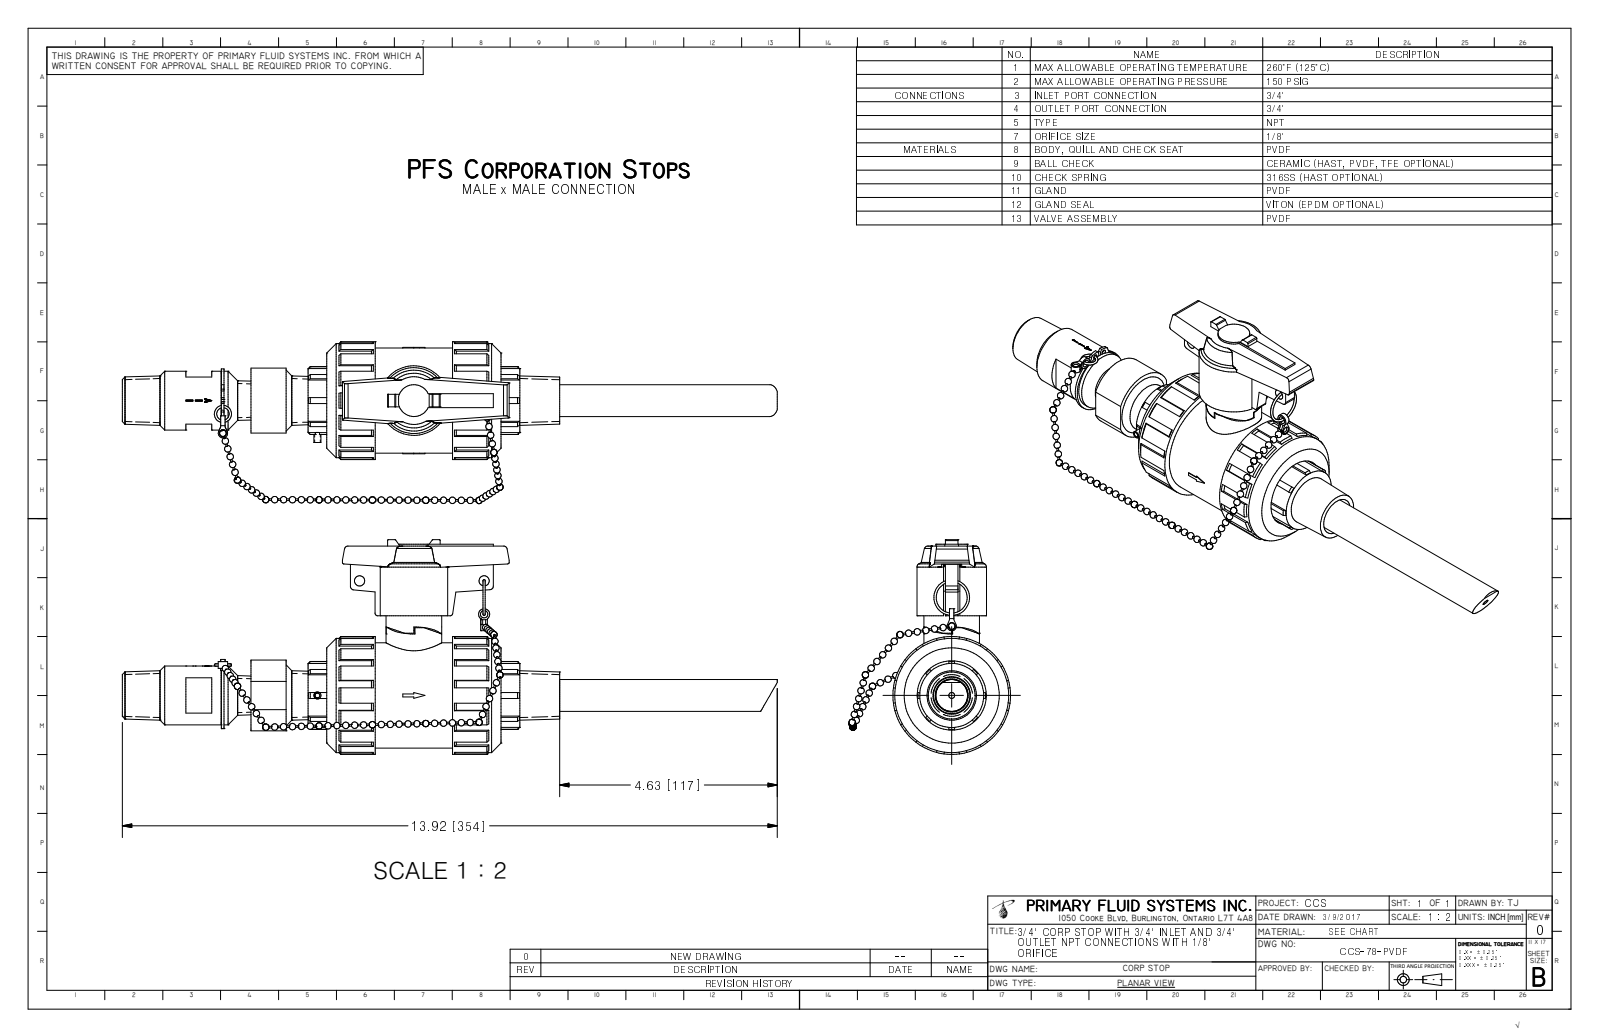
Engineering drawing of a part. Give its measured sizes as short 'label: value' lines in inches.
name: CCS-78-PVDF_R0
written by: Autodesk Inventor 2009 (AUTOMOTIVE_DESIGN)
unit: in
bodies: 1 solid, 613 faces (293 planar, 78 cylindrical, 242 other)
size: 13.922 × 4.554 × 3.436
volume: 26.76 in³; area: 125.7 in²
holes: 1× ⌀0.098, 1× ⌀0.125, 1× ⌀0.217, 1× ⌀0.25, 1× ⌀0.469, 1× ⌀0.56, 1× ⌀1.47, 1× ⌀2.16
bosses: 1× ⌀2.5, 1× ⌀2.422, 1× ⌀2.232, 1× ⌀1.801, 1× ⌀1.476, 1× ⌀1.36, 1× ⌀1.343, 1× ⌀1.25
rounds: 4× R0.02, 4× R0.079, 2× R0.039, 2× R0.054, 2× R0.059, 2× R0.197, 1× R0.337, 1× R0.624
face distances: 0.039, 0.266, 0.306, 0.472, 3.233, 0.23, 3.475, 0.242, 3.003, 1.03
hole spacings: 0.657
